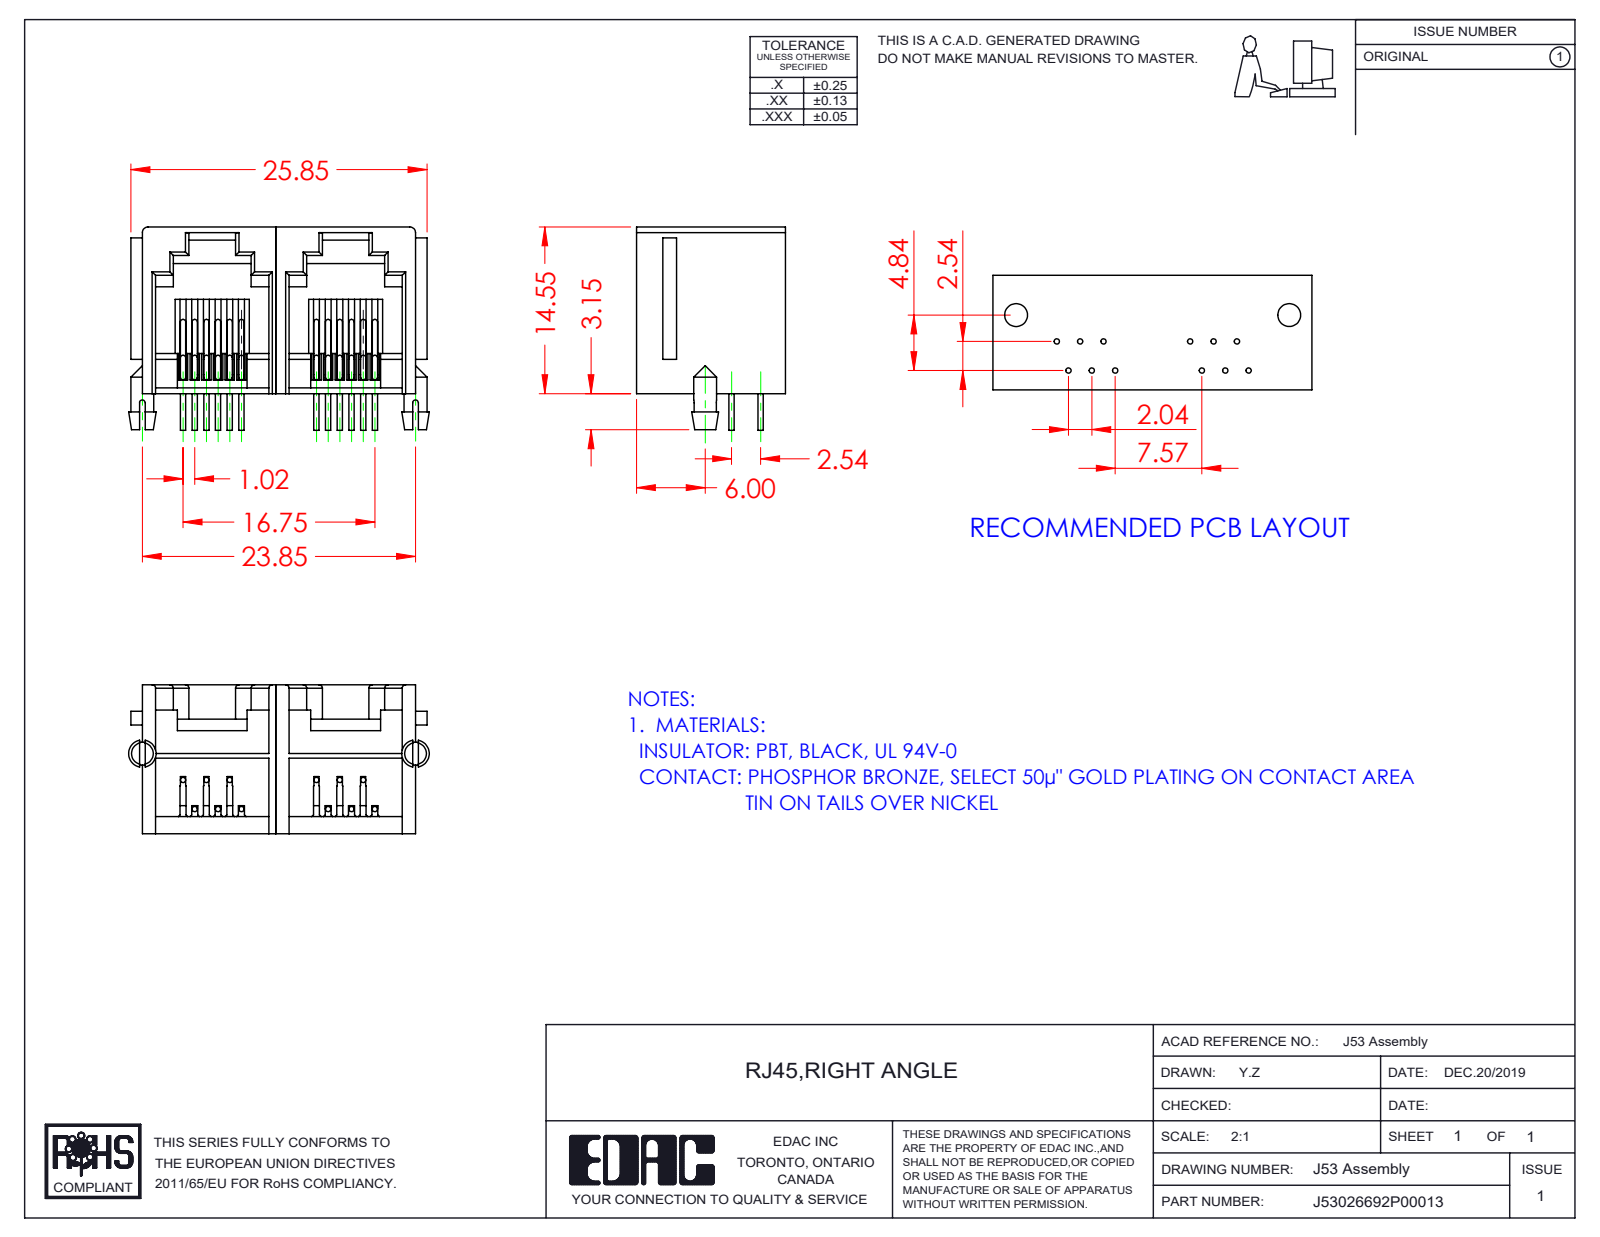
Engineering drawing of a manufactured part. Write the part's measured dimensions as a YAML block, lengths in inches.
part_name: "53 Contact - 2; 53 Insulator LH; 53 Contact - 4; 53 Contacts (+6 more)"
step_written_by: "SolidWorks 2016 (CONFIG_CONTROL_DESIGN)"
units: inches
bodies: {solids: 14, faces: 595, planar: 410, cylindrical: 128, other: 57}
overall_size: [1.033, 0.699, 0.512]
volume: 0.11
surface_area: 6.634
round_bosses_or_shafts:
  - {diameter: 0.018, count: 36}
  - {diameter: 0.079, count: 2}
partial_cylinders:
  - {radius: 0.012, count: 14}
  - {radius: 0.02, count: 10}
  - {radius: 0.01, count: 2}
  - {radius: 0.026, count: 1}
face_to_face_distances: [0.459, 0.046, 0.435, 0.48, 0.893, 0.413, 0.504, 0.024, 0.389, 0.118]
